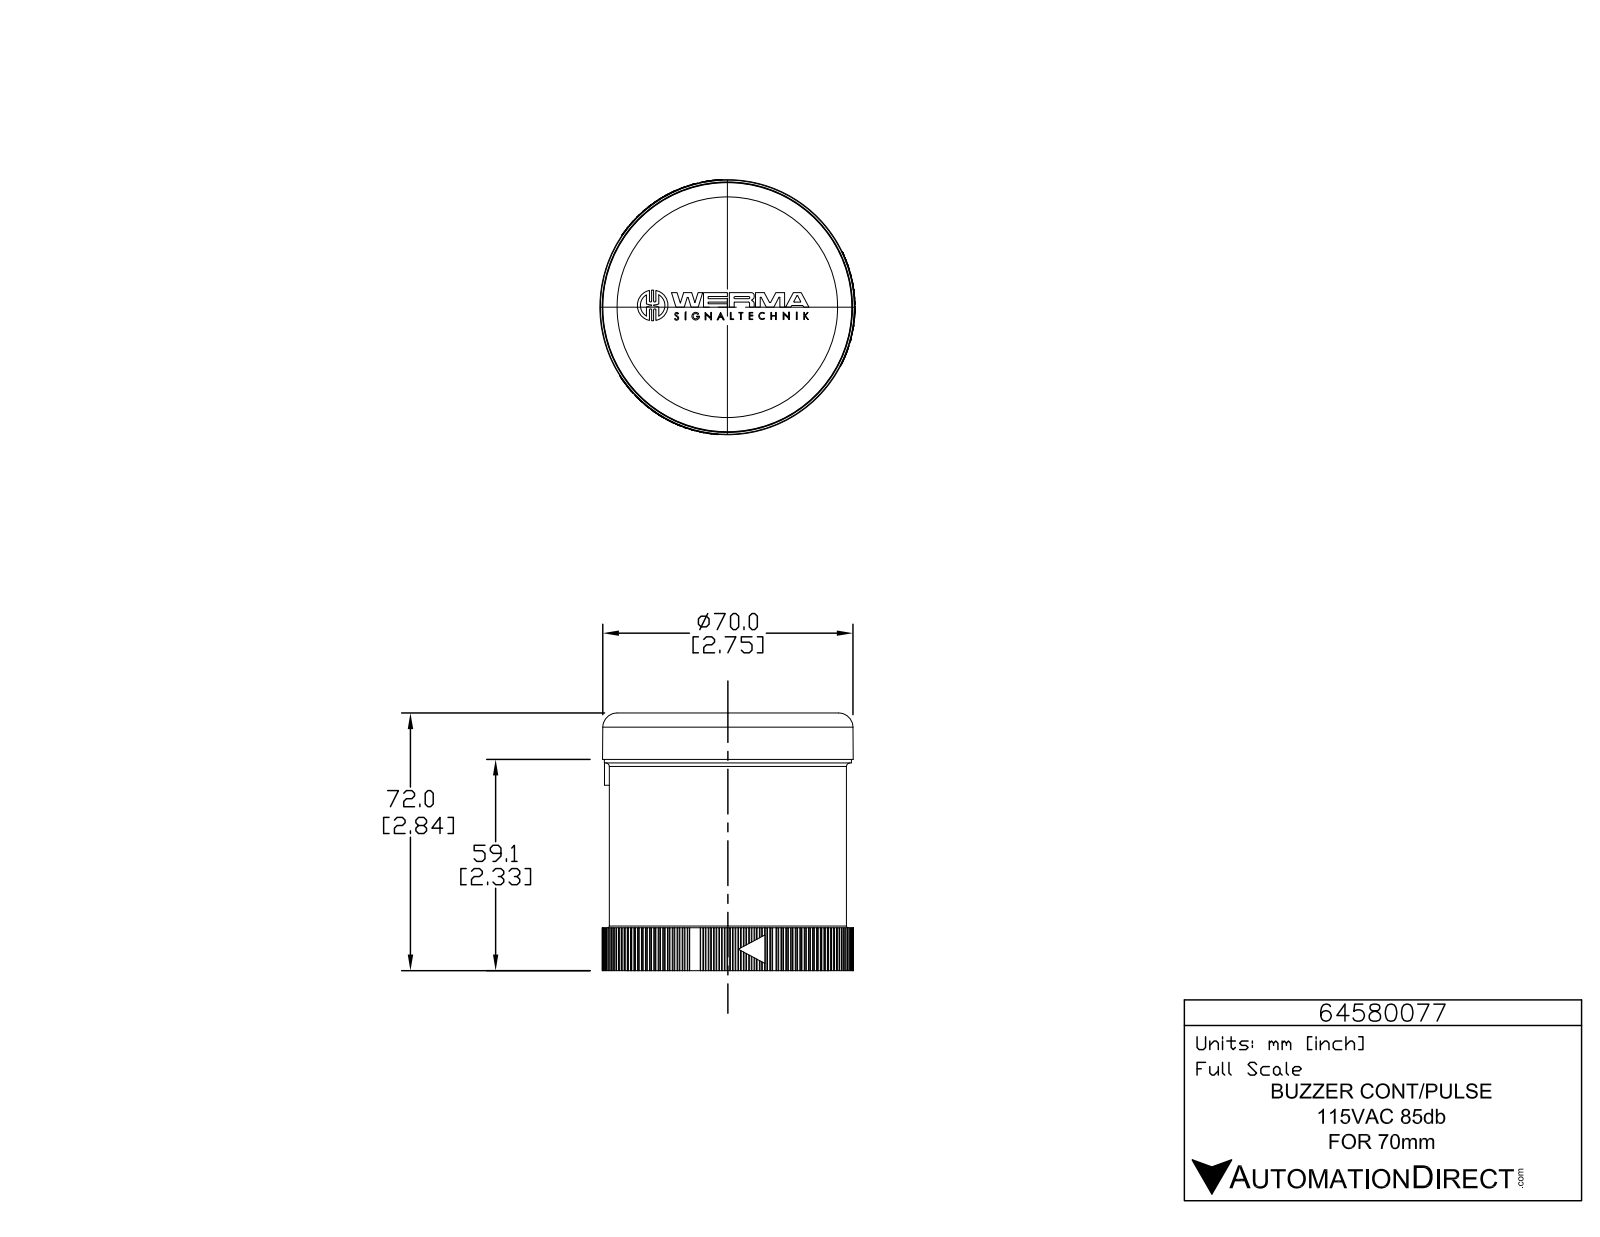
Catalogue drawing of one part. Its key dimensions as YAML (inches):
part_name: "64580077"
step_written_by: "SolidWorks 2015 (AUTOMOTIVE_DESIGN)"
units: inches
bodies: {solids: 1, faces: 1402, planar: 832, cylindrical: 563, other: 7}
overall_size: [2.762, 2.762, 2.705]
volume: 13.05
surface_area: 38.6
round_holes:
  - {diameter: 0.039, count: 3}
  - {diameter: 2.575, count: 1}
round_bosses_or_shafts:
  - {diameter: 0.226, count: 3}
  - {diameter: 0.056, count: 3}
  - {diameter: 2.762, count: 1}
  - {diameter: 2.717, count: 1}
  - {diameter: 2.606, count: 1}
partial_cylinders:
  - {radius: 0.008, count: 285}
  - {radius: 0.008, count: 6}
  - {radius: 0.008, count: 6}
  - {radius: 0.008, count: 6}
  - {radius: 0.131, count: 6}
  - {radius: 0.004, count: 3}
  - {radius: 0.005, count: 3}
  - {radius: 0.008, count: 3}
face_to_face_distances: [2.327, 2.451, 0.378, 2.705, 2.452, 0.472, 0.094, 2.232, 2.452, 2.452]
